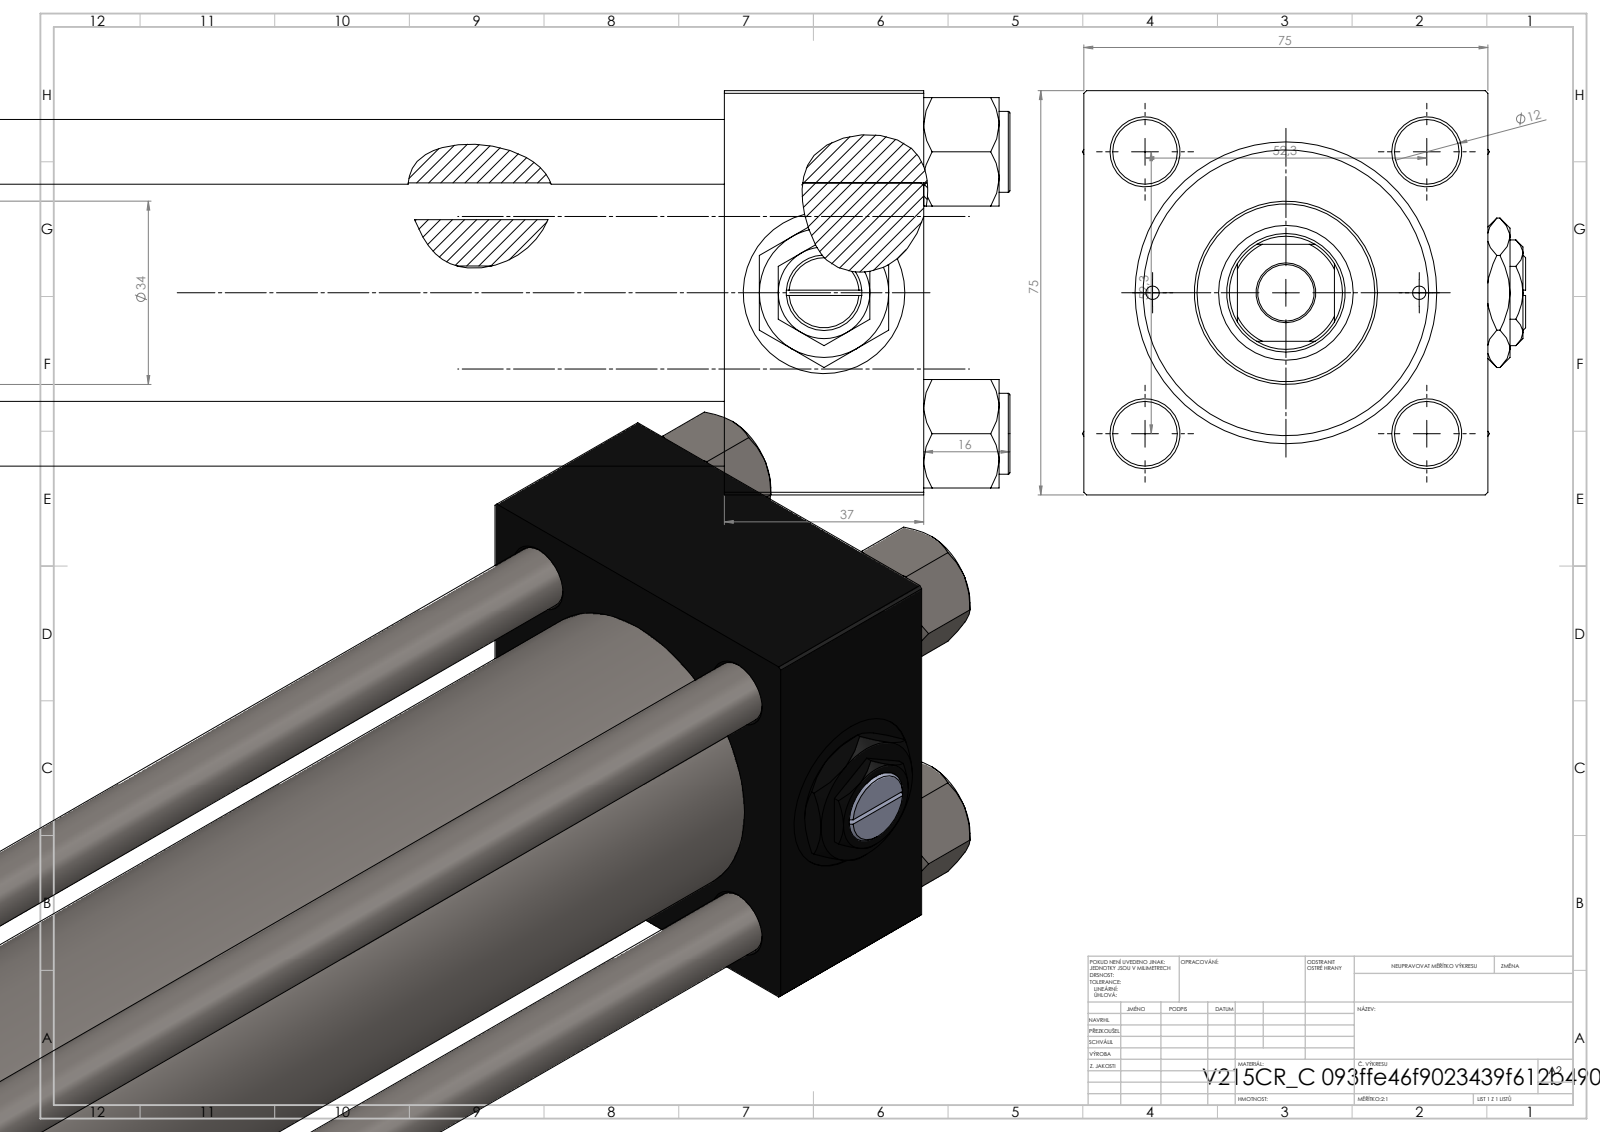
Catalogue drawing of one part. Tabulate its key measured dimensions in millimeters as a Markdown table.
| quantity | value |
| --- | --- |
| part name | V215CR_VCP_C; V215CR_C_Body; Zatka_pro_OIL_PORT; V215_VC_A (+2 more) |
| STEP written by | SolidWorks 2019 (CONFIG_CONTROL_DESIGN) |
| units | millimeters |
| bodies | 13 solids, 1255 faces (575 planar, 102 cylindrical, 578 other) |
| overall size | 425 × 82.27 × 75 |
| volume | 958 157 mm³ |
| surface area | 279 013 mm² |
| round holes (diameter × count) | 12 × 4, 2.5 × 2, 7 × 2, 20.96 × 2, 30 × 2, 10.5 × 1, 22 × 1, 25 × 1, 41 × 1, 50 × 1, 53 × 1 |
| round bosses / shafts (diameter × count) | 15 × 4, 56 × 1, 34 × 1 |
| partial cylindrical surfaces (radius × count) | 10.5 × 1 |
| main face-to-face distances | 75, 37, 384, 347, 325, 288, 59, 355.3, 318.3, 30.3 |
| hole center spacings | 26.19, 36.98, 52.3, 57.22, 24.75, 73.96, 49.5, 323.5 |
